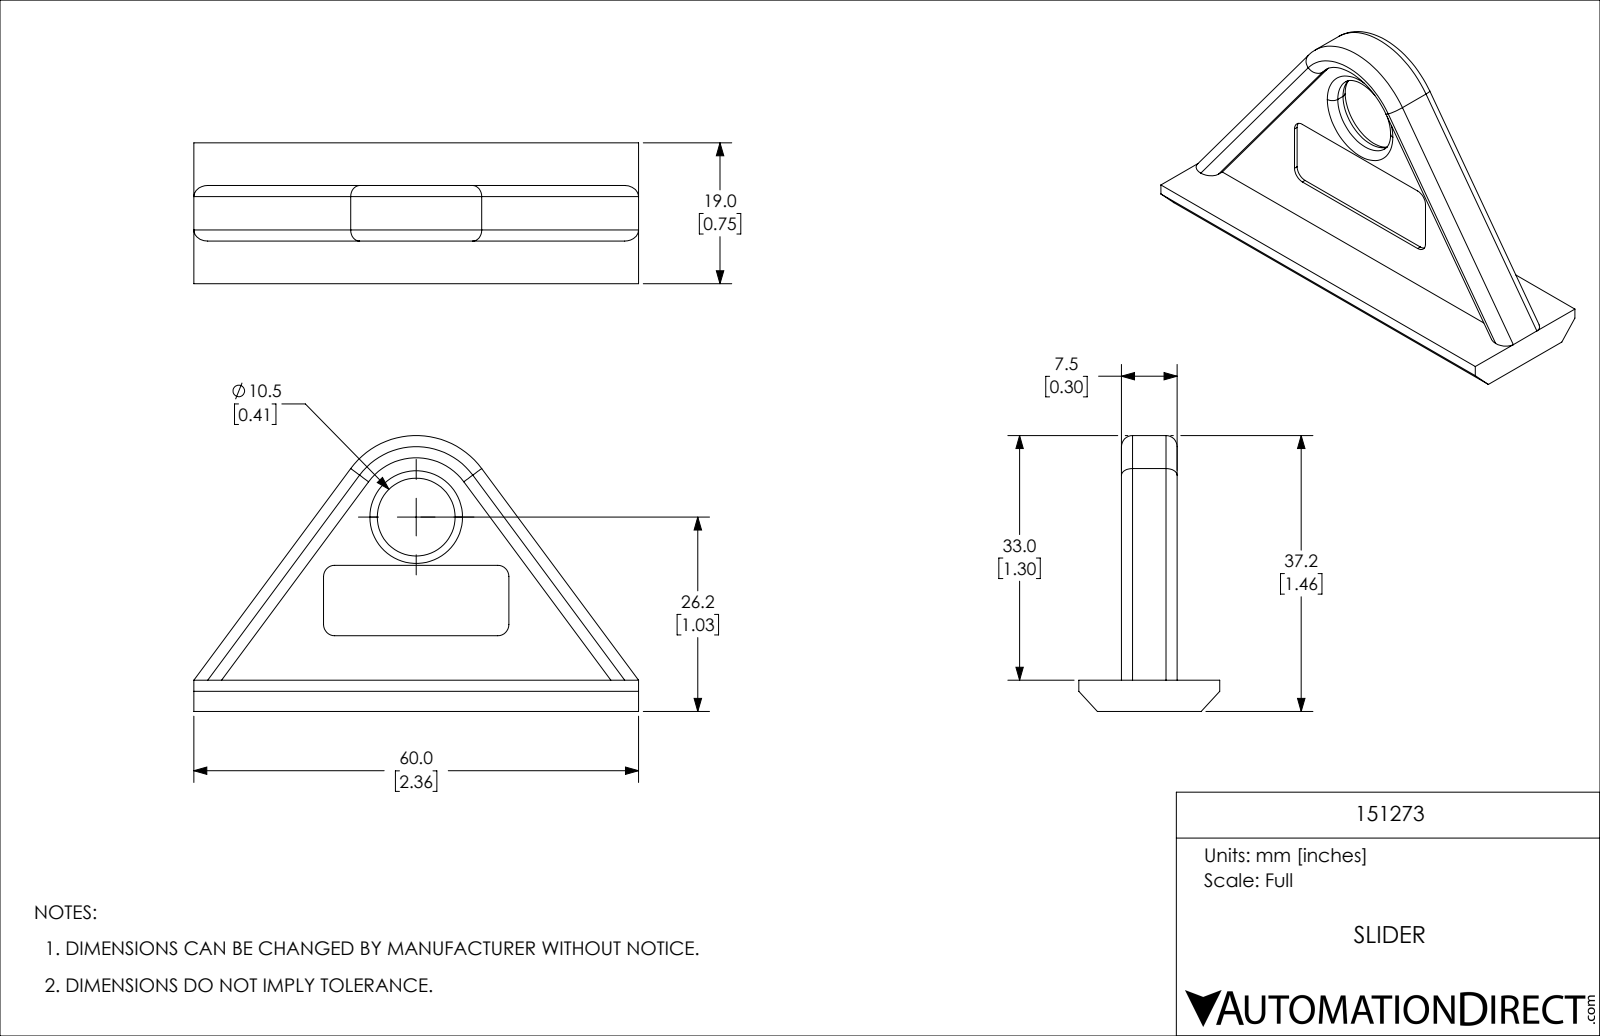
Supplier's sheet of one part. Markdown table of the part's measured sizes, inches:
| quantity | value |
| --- | --- |
| part name | 151273 |
| STEP written by | SolidWorks 2023 (CONFIG_CONTROL_DESIGN) |
| units | inches |
| bodies | 1 solid, 146 faces (40 planar, 32 cylindrical, 74 other) |
| overall size | 2.362 × 1.465 × 0.669 |
| volume | 0.547 in³ |
| surface area | 8.882 in² |
| round holes (diameter × count) | 0.413 × 1 |
| partial cylindrical surfaces (radius × count) | 0.02 × 20, 0.059 × 4, 0.1 × 4 |
| main face-to-face distances | 0.167, 0.118, 0.202, 0.084, 0.083, 0.202, 0.285, 0.276, 0.394, 0.192 |
